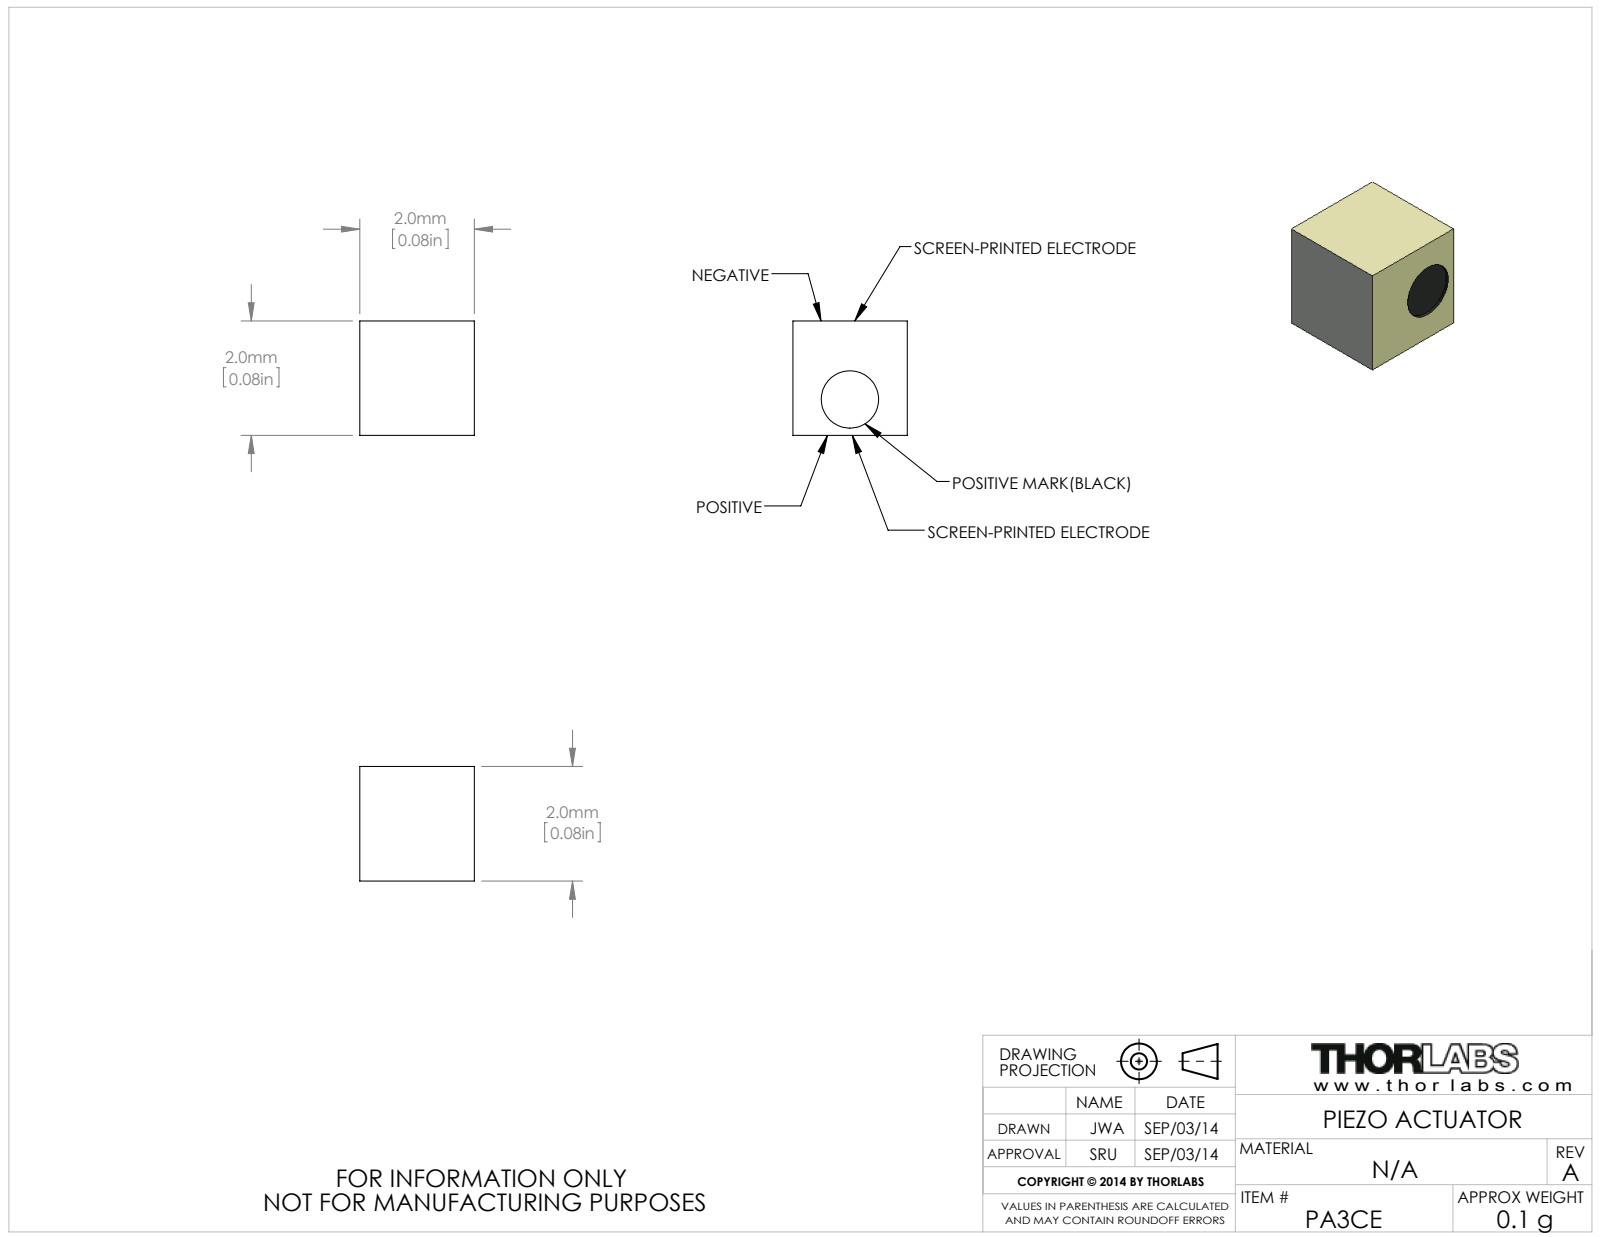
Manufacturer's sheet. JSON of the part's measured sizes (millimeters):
{"part_name": "PA3CE", "step_written_by": "SolidWorks 2012 (AUTOMOTIVE_DESIGN)", "units": "millimeters", "bodies": {"solids": 1, "faces": 9, "planar": 7, "cylindrical": 2, "other": 0}, "overall_size": [2, 2, 2], "volume_mm3": 8, "surface_area_mm2": 24, "round_holes": [[1, 1]], "face_to_face_distances": [2, 1.95]}
